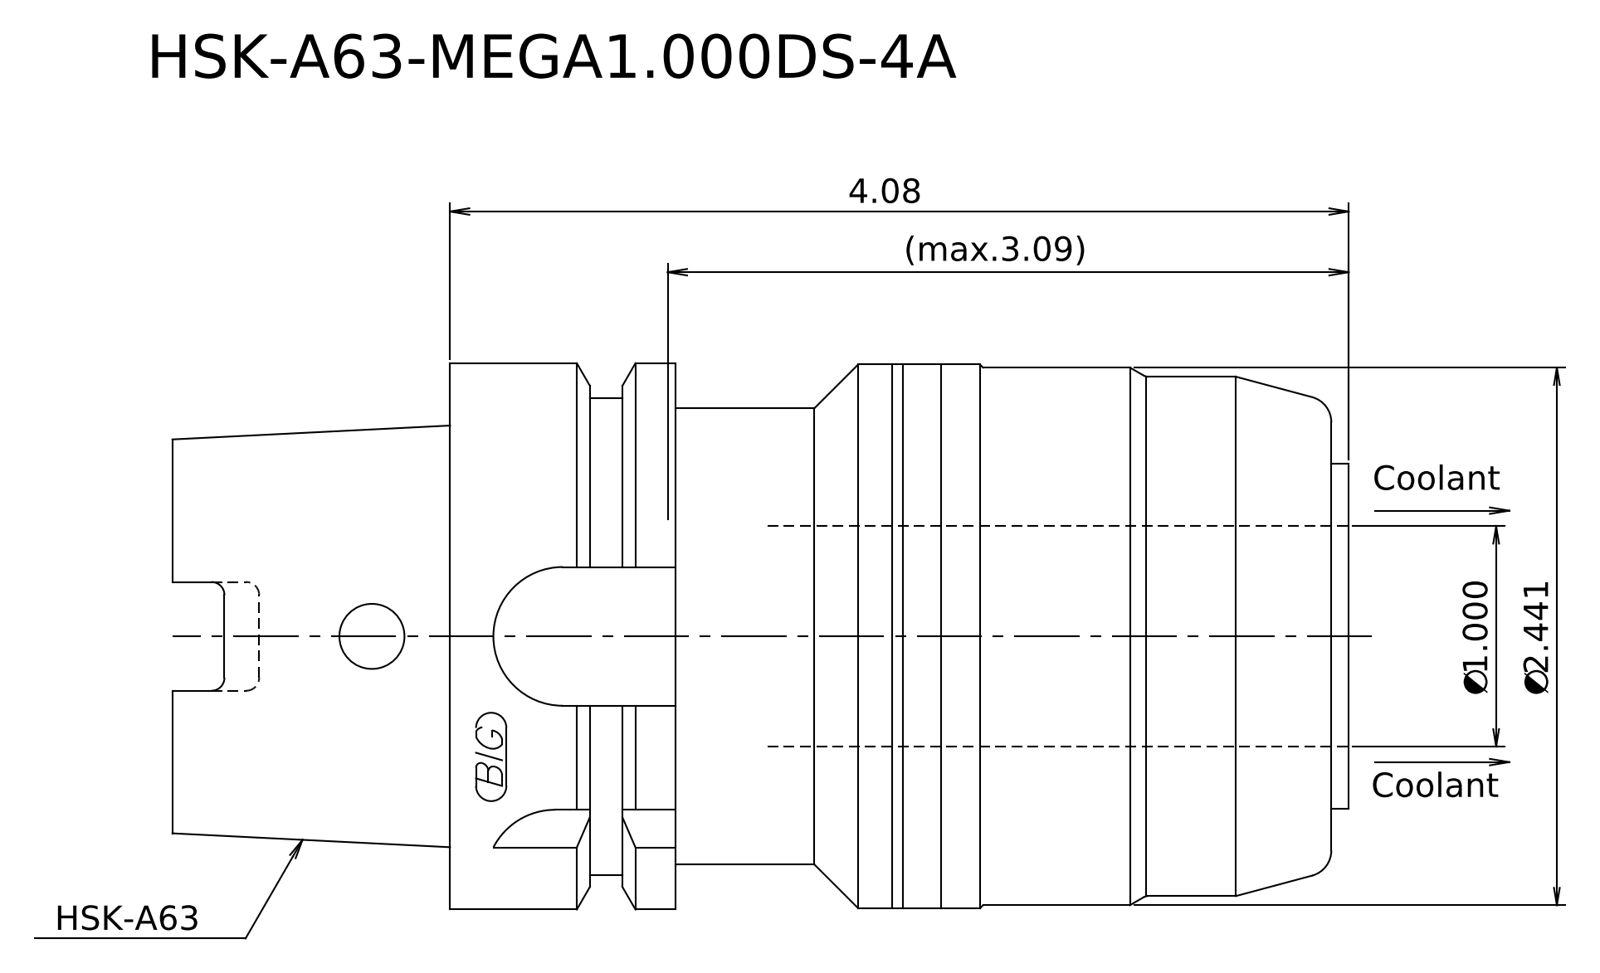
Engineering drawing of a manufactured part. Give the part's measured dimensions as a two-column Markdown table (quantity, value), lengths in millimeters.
| quantity | value |
| --- | --- |
| part name | HSK-A63-MEGA1.000DS-4A |
| STEP written by | SolidWorks 2016 (CONFIG_CONTROL_DESIGN) |
| units | millimeters |
| bodies | 1 solid, 89 faces (35 planar, 21 cylindrical, 33 other) |
| overall size | 135.6 × 63 × 63 |
| volume | 249 829 mm³ |
| surface area | 42 678 mm² |
| round holes (diameter × count) | 7.5 × 1, 16.5 × 1, 25.4 × 1, 34 × 1, 34.5 × 1, 40 × 1 |
| round bosses / shafts (diameter × count) | 63 × 1, 62.7 × 1, 62 × 1, 59.9 × 1, 55 × 1, 53 × 1, 39.84 × 1 |
| partial cylindrical surfaces (radius × count) | 4.34 × 1, 8 × 1, 9 × 1 |
| main face-to-face distances | 26, 101.6, 75.6, 16, 10, 91.6, 103.6, 93.6, 77.6, 2 |
